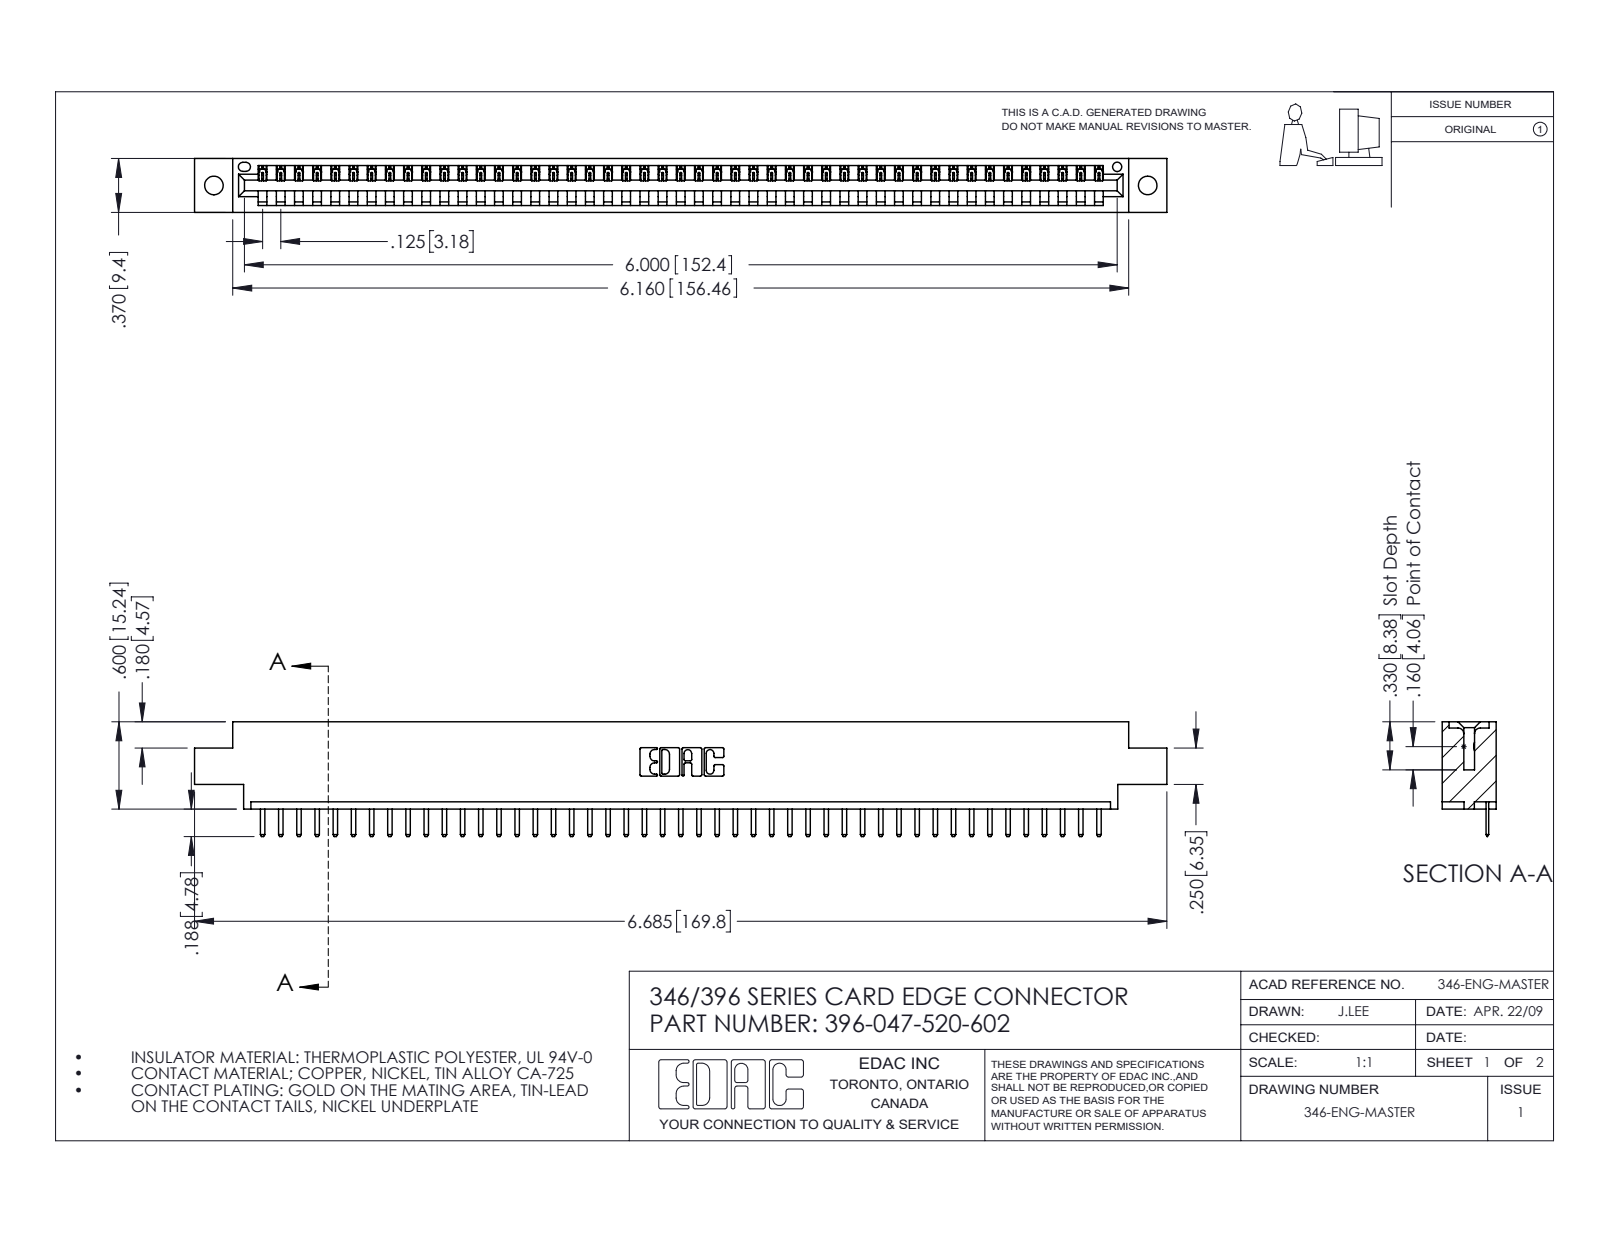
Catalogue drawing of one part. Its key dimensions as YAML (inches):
part_name: "345-292-001_345-293-120; 346 Part_0.170 Offset - 0.128 Dia; 396-047-520-602"
step_written_by: "SolidWorks 2016 (CONFIG_CONTROL_DESIGN)"
units: inches
bodies: {solids: 48, faces: 3040, planar: 2054, cylindrical: 986, other: 0}
overall_size: [6.685, 0.788, 0.37]
volume: 0.974
surface_area: 30.13
round_holes:
  - {diameter: 0.128, count: 2}
  - {diameter: 0.064, count: 1}
partial_cylinders:
  - {radius: 0.01, count: 96}
  - {radius: 0.006, count: 94}
  - {radius: 0.01, count: 22}
  - {radius: 0.007, count: 6}
  - {radius: 0.031, count: 6}
  - {radius: 0.026, count: 3}
  - {radius: 0.031, count: 2}
  - {radius: 0.04, count: 2}
face_to_face_distances: [0.048, 0.322, 0.37, 0.25, 0.148, 0.222, 0.1, 0.174, 0.072, 0.298]
hole_center_spacings: [0.246, 6.211, 6.42]
